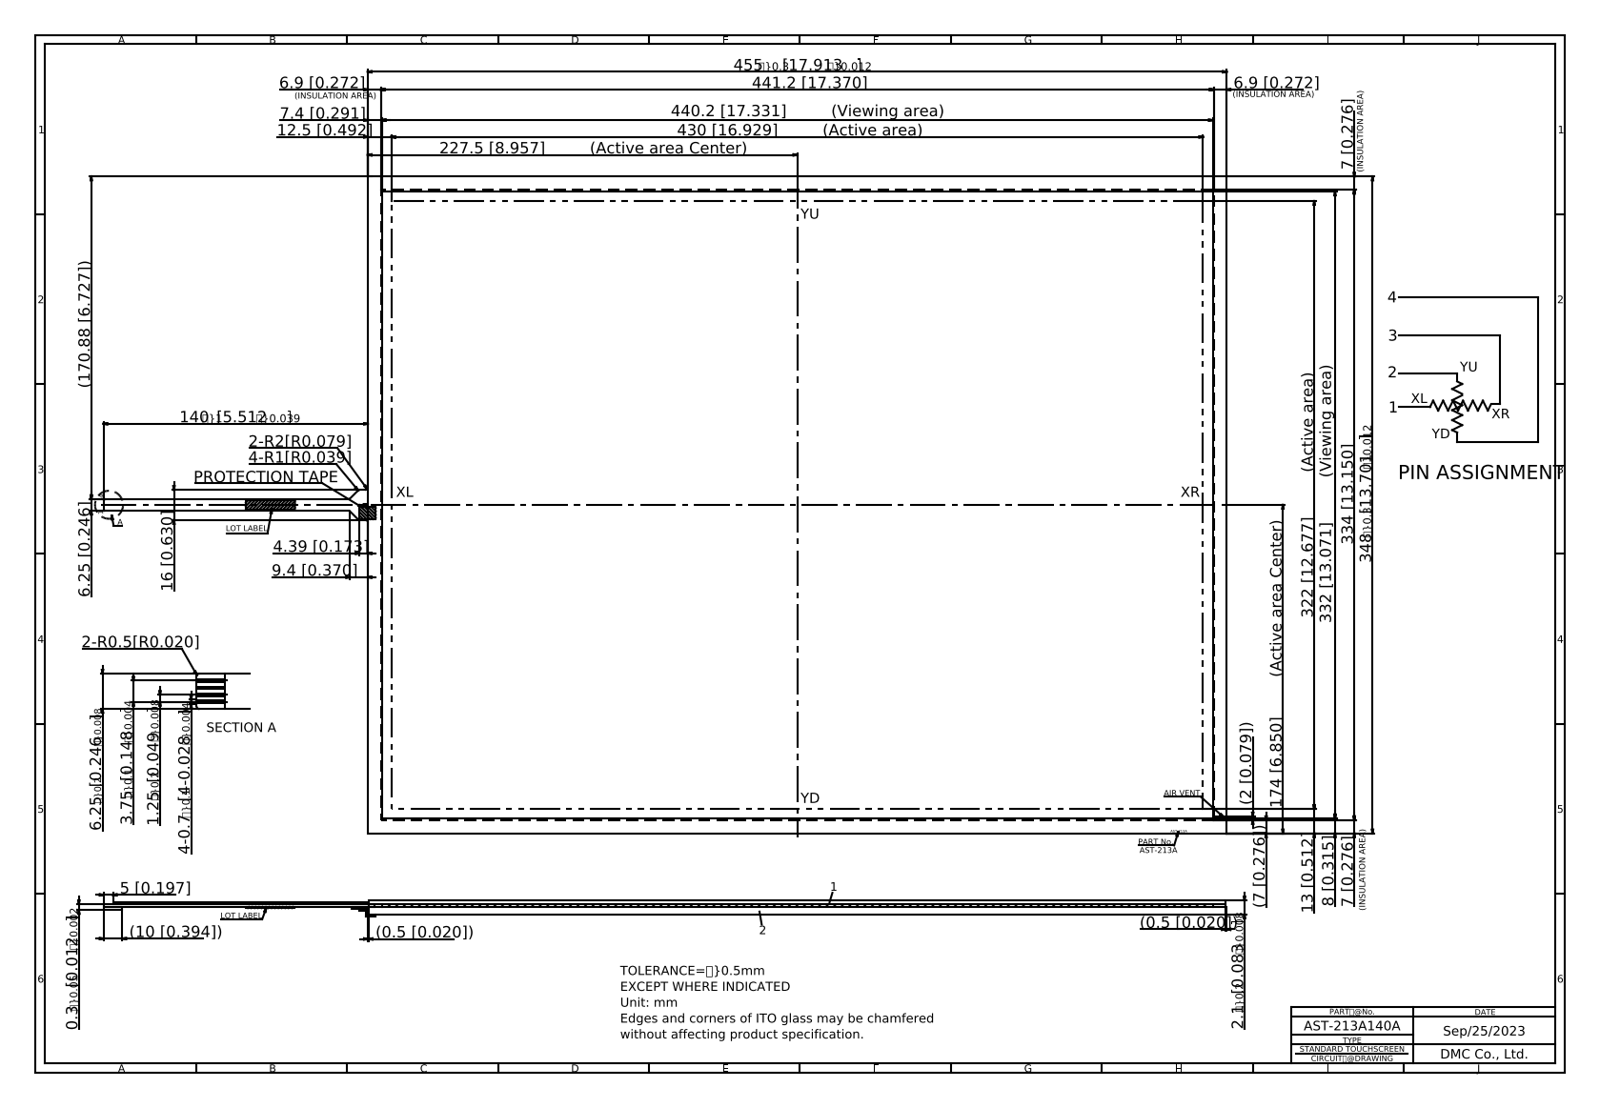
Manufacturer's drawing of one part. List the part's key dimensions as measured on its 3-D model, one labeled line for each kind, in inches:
Part name (STEP PRODUCT): AST-213A140A
STEP written by: Autodesk Inventor 2020 (CONFIG_CONTROL_DESIGN)
Units: inches
Bodies: 1 solid, 51 faces (45 planar, 6 cylindrical, 0 other)
Overall size (bounding box): 27.008 × 19.181 × 0.083
Volume: 20.25 in³ · Surface area: 499.5 in²
Partial cylindrical surfaces — rounded edges, fillets, slot ends (radius × count): R0.039 ×4, R0.02 ×2
Main face-to-face distances: 0.083, 0.079, 13.701, 0.075, 0.071, 17.913, 0.315, 13.386, 0.197, 0.512
